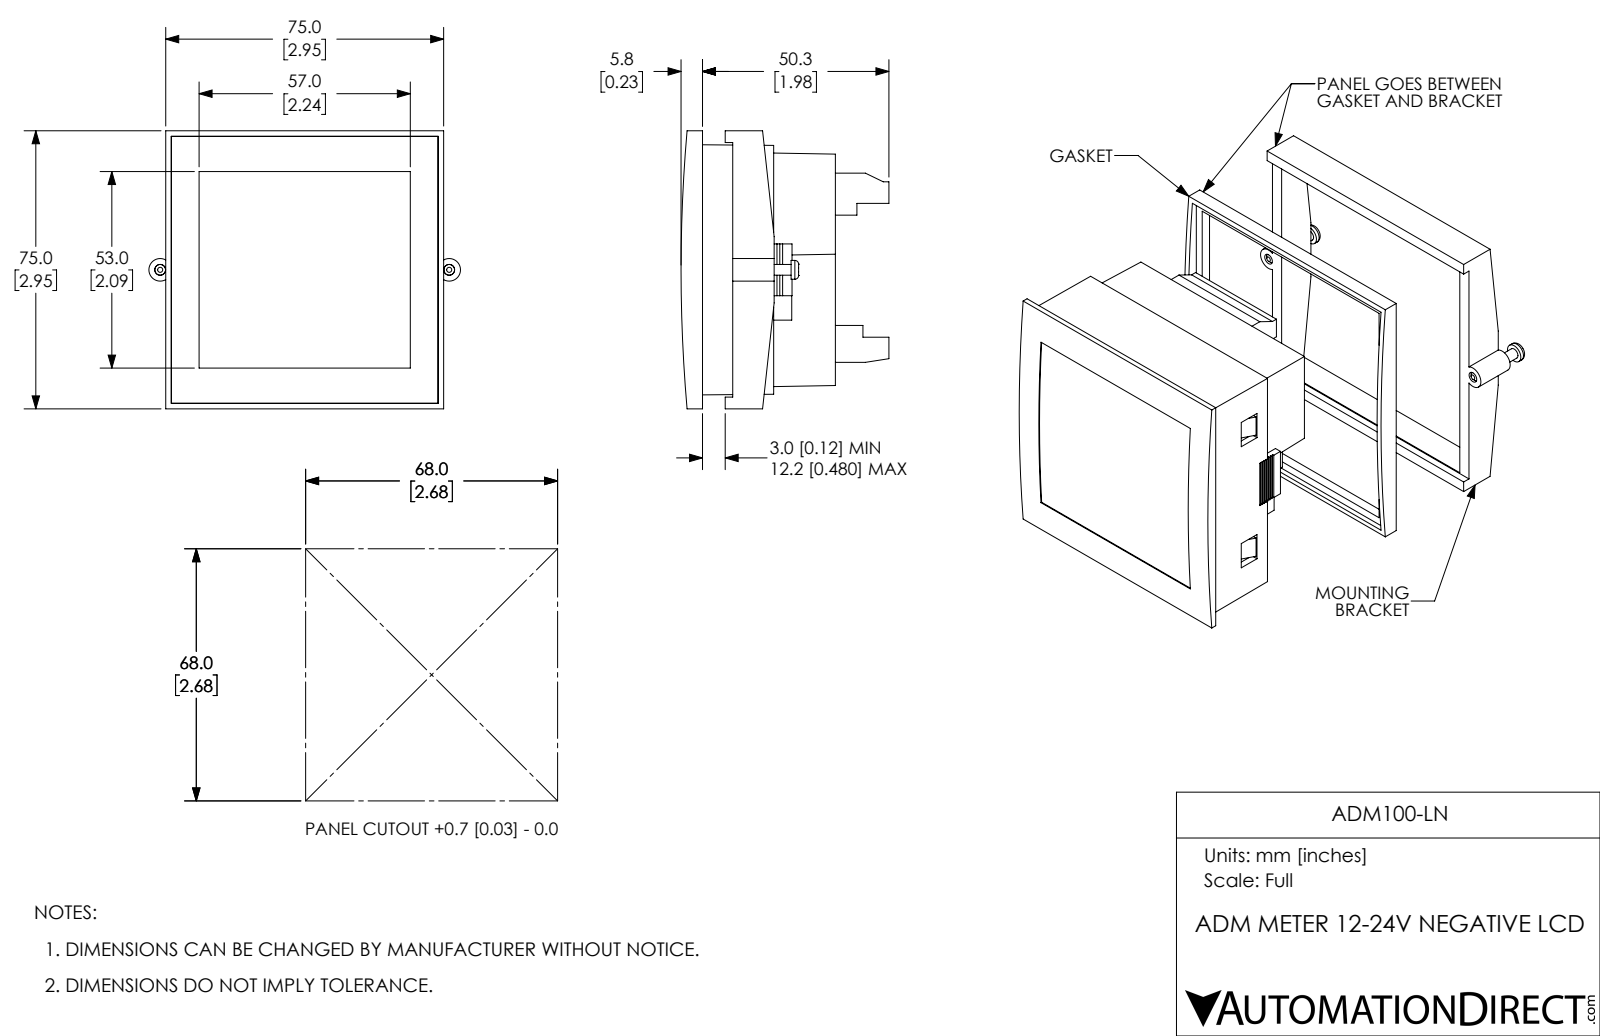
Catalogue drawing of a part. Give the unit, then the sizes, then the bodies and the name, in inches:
Units: inches
Overall size (bounding box): 3.311 × 2.953 × 2.209
Round holes (diameter × count): ⌀0.151 ×13, ⌀0.115 ×2
Round bosses / shafts (diameter × count): ⌀0.148 ×13, ⌀0.2 ×2, ⌀0.114 ×2
Partial cylindrical surfaces — rounded edges, fillets, slot ends (radius × count): R0.12 ×2, R17.037 ×2
Main face-to-face distances: 0.075, 0.305, 0.236, 2.717, 2.657, 0.089, 0.148, 2.805, 2.583, 1.142
Hole centre spacings: 1.653, 0.2, 1.677, 0.4, 1.724, 0.6, 1.792, 0.8
Volume: 9.565 in³ · Surface area: 90.64 in²
Bodies: 23 solids, 419 faces (335 planar, 76 cylindrical, 8 other)
Part name (STEP PRODUCT): ADM100-LN
STEP written by: SolidWorks 2017 (AUTOMOTIVE_DESIGN)
